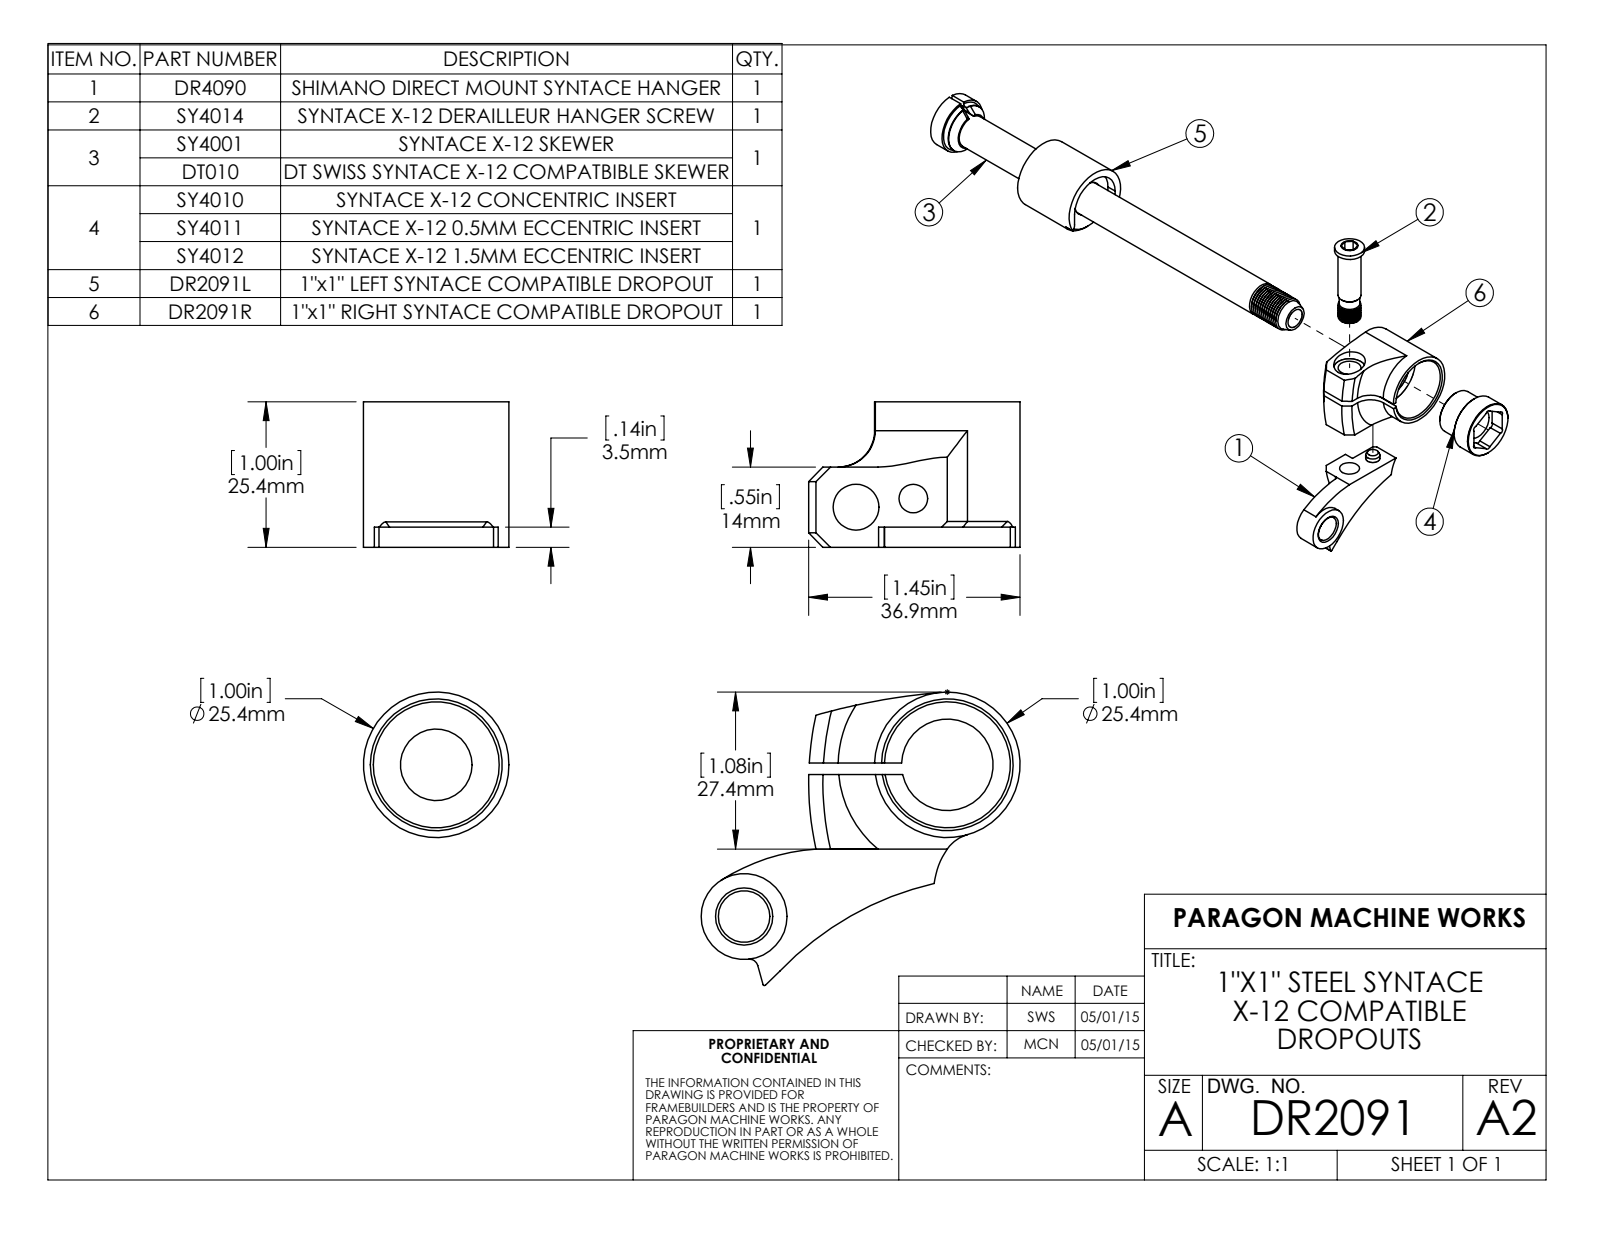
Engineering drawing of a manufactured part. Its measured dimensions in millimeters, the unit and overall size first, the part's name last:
Units: millimetres
Overall size (bounding box): 185.55 × 55.69 × 51.24
Round holes (diameter × count): ⌀7 ×2, ⌀11 ×2, ⌀4 ×1, ⌀5 ×1, ⌀8 ×1, ⌀9 ×1, ⌀12 ×1, ⌀12.5 ×1, ⌀16 ×1, ⌀22 ×1
Round bosses / shafts (diameter × count): ⌀15 ×2, ⌀25.4 ×1, ⌀20 ×1, ⌀17.7 ×1, ⌀16.05 ×1, ⌀15.4 ×1, ⌀10.5 ×1, ⌀7.25 ×1
Partial cylindrical surfaces — rounded edges, fillets, slot ends (radius × count): R1 ×9, R2.5 ×3, R3.61 ×2, R0.25 ×1, R1.5 ×1, R6.49 ×1, R13 ×1, R35.52 ×1
Main face-to-face distances: 3.5, 4.5, 14, 8, 12.5, 10.5, 1.5, 2, 138.25, 150.75
Hole centre spacings: 10.11, 44.27
Volume: 34 808 mm³ · Surface area: 27 783 mm²
Bodies: 8 solids, 325 faces (69 planar, 97 cylindrical, 159 other)
Part name (STEP PRODUCT): SY4014; DR4090; cone_for_12mm_axle_ver-02; 12mm_Axle_ver-01 (+5 more)
STEP written by: SolidWorks 2015 (AUTOMOTIVE_DESIGN)
